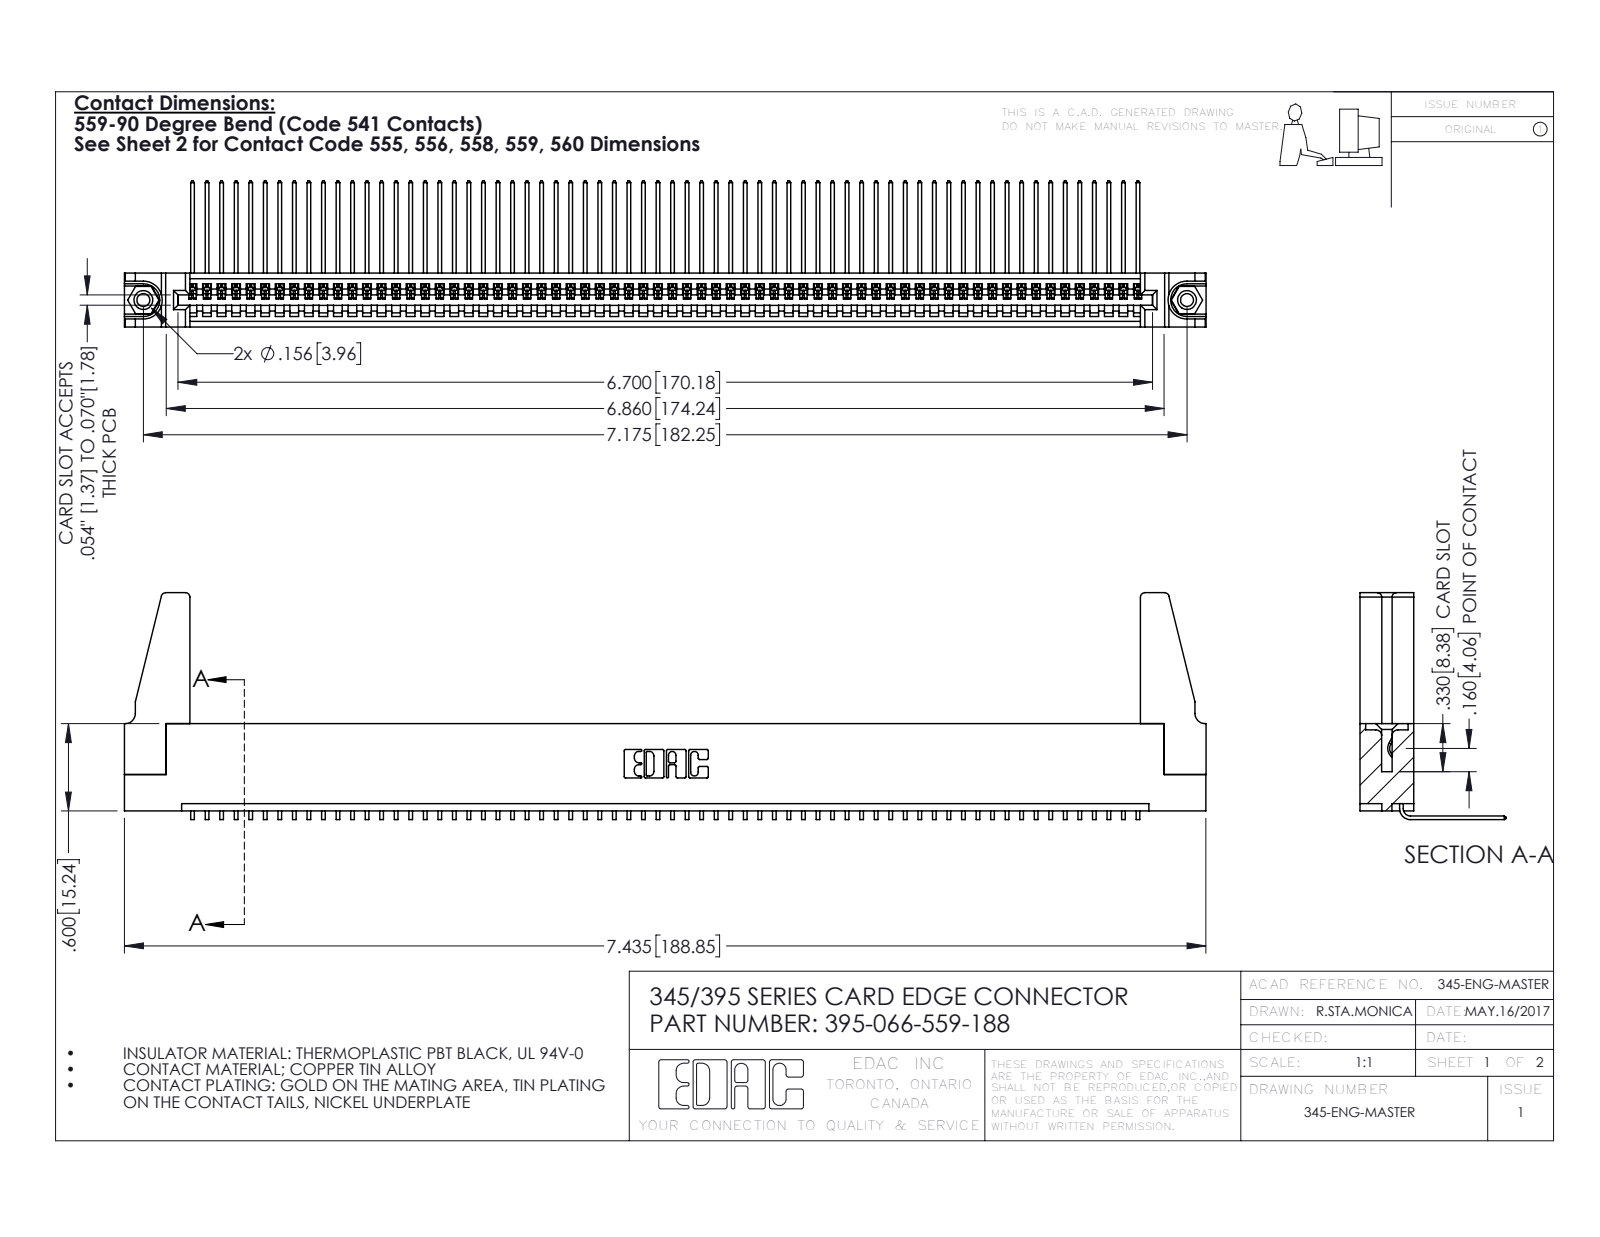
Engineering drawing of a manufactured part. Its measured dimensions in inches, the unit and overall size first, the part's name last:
Units: inches
Overall size (bounding box): 7.436 × 1.559 × 1.005
Round holes (diameter × count): ⌀0.089 ×2, ⌀0.125 ×2, ⌀0.156 ×2, ⌀0.064 ×1
Round bosses / shafts (diameter × count): ⌀0.155 ×2
Partial cylindrical surfaces — rounded edges, fillets, slot ends (radius × count): R0.006 ×132, R0.01 ×22, R0.03 ×8, R0.007 ×6, R0.031 ×6, R0.026 ×3, R0.031 ×2, R0.04 ×2
Main face-to-face distances: 0.072, 0.298, 0.37, 0.2, 0.098, 0.272, 0.025, 0.225, 0.149, 0.072
Hole centre spacings: 0.27, 6.939, 7.175
Volume: 1.319 in³ · Surface area: 45.17 in²
Bodies: 71 solids, 4210 faces (2924 planar, 1270 cylindrical, 16 other)
Part name (STEP PRODUCT): 345-220-078_345-220-088; 345 Part_Flush Mounting Lugs - 0.156 Dia-TH; 345-250-001_345-250-001-102; 345-292-001_558 559 Tail - 1 (+1 more)
STEP written by: SolidWorks 2016 (CONFIG_CONTROL_DESIGN)
